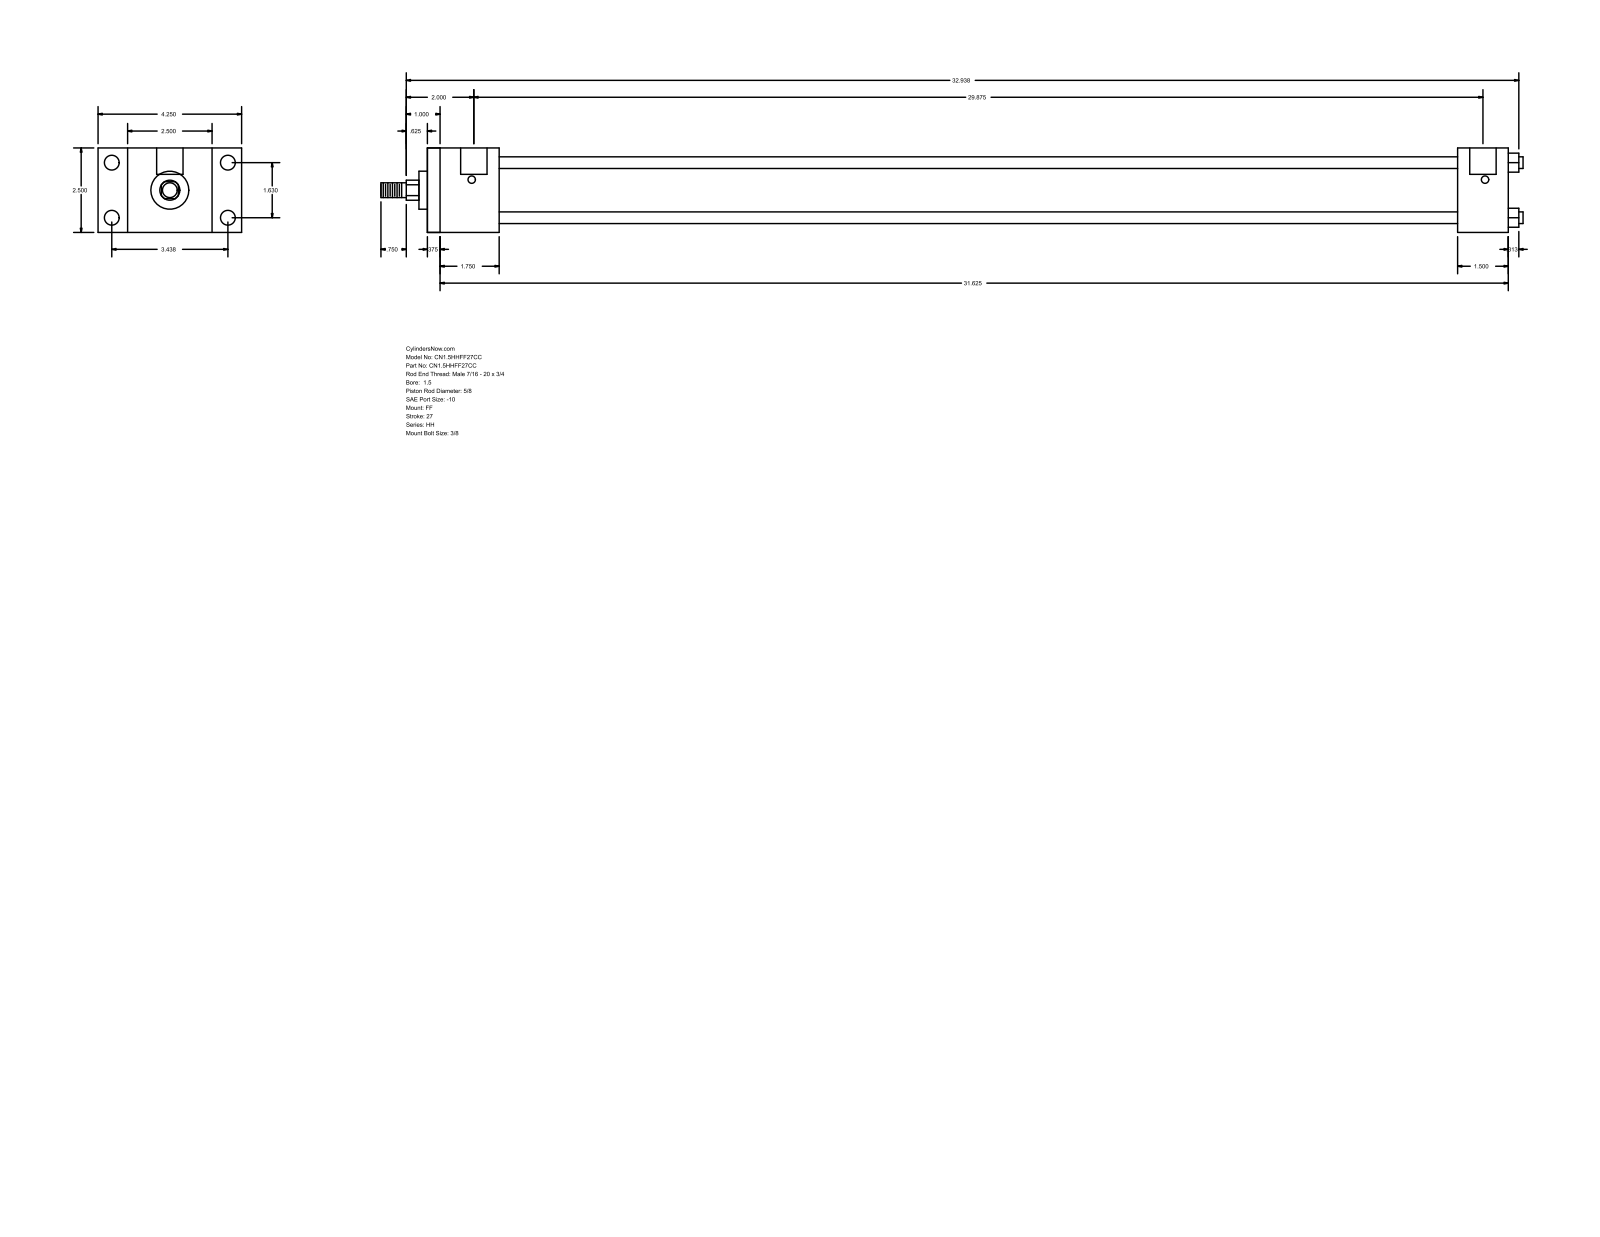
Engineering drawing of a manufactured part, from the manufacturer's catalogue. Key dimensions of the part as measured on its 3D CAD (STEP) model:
Part name (STEP PRODUCT): HH_FF__0150_0.625
STEP written by: GSSL Pune (CONFIG_CONTROL_DESIGN)
Units: millimetres
Bodies: 0 solids, 92 faces (64 planar, 28 cylindrical, 0 other)
Overall size (bounding box): 858.84 × 107.95 × 63.5
Round holes (diameter × count): ⌀5.56 ×4, ⌀11.13 ×4, ⌀19.84 ×2
Round bosses / shafts (diameter × count): ⌀8.76 ×4, ⌀44.45 ×1, ⌀28.57 ×1, ⌀15.88 ×1, ⌀11.11 ×1
Partial cylindrical surfaces — rounded edges, fillets, slot ends (radius × count): R7.54 ×1
Main face-to-face distances: 63.5, 812.79, 9.52, 803.27, 44.45, 53.97, 758.82, 774.7, 765.18, 720.73
Hole centre spacings: 1.59, 41.4, 87.32, 96.64, 760.41, 762, 758.82
